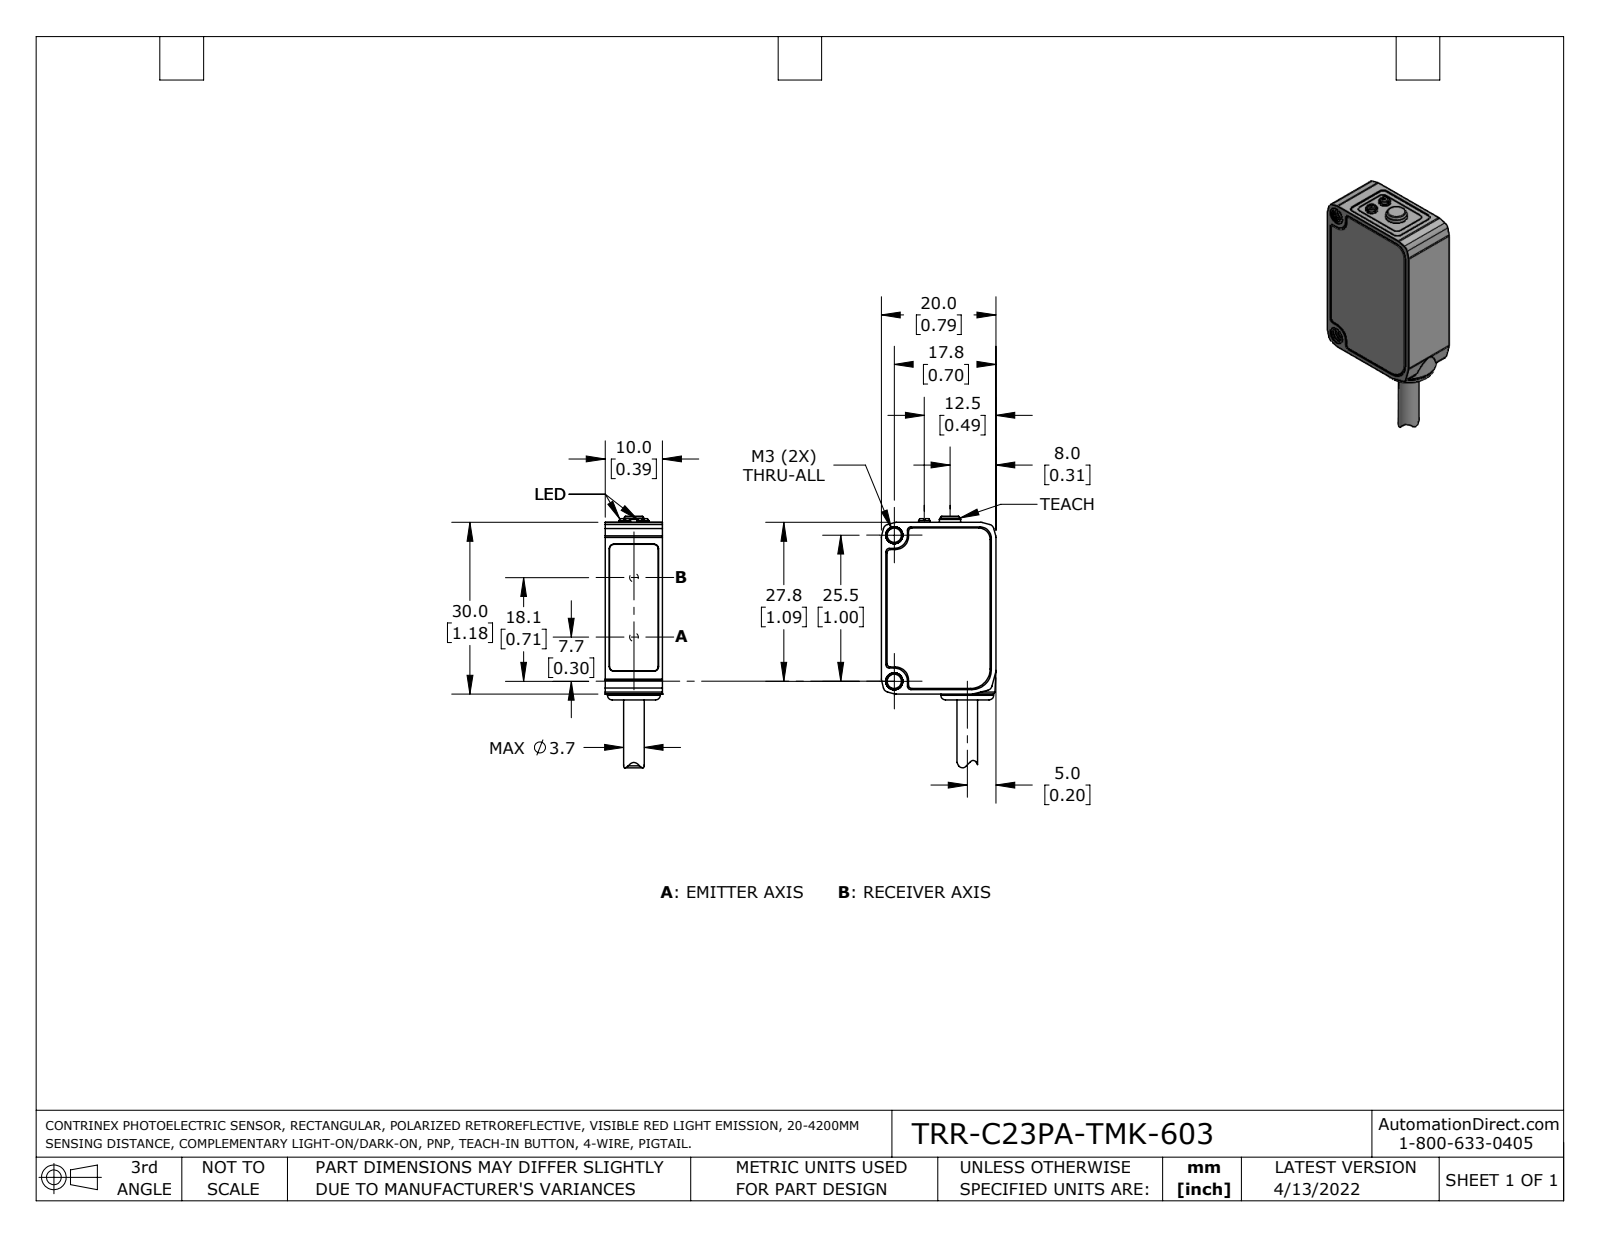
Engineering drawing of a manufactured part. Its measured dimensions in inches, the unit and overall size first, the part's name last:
Units: inches
Overall size (bounding box): 1.728 × 0.787 × 0.394
Round holes (diameter × count): ⌀0.098 ×2, ⌀0.142 ×2
Round bosses / shafts (diameter × count): ⌀0.079 ×2, ⌀0.362 ×1, ⌀0.146 ×1, ⌀0.142 ×1
Partial cylindrical surfaces — rounded edges, fillets, slot ends (radius × count): R0.031 ×20, R0.039 ×11, R0.024 ×8, R0.091 ×4, R0.134 ×3, R0.079 ×2, R0.025 ×1, R0.033 ×1
Main face-to-face distances: 0.394, 0.785, 0.039, 0.787, 1.181, 1.177, 1.217, 1.22, 0.028, 1.219
Hole centre spacings: 1.004
Volume: 0.365 in³ · Surface area: 4.154 in²
Bodies: 1 solid, 269 faces (87 planar, 136 cylindrical, 46 other)
Part name (STEP PRODUCT): TRR-C23PA-TMK-603
STEP written by: SolidWorks 2021 (AUTOMOTIVE_DESIGN)
